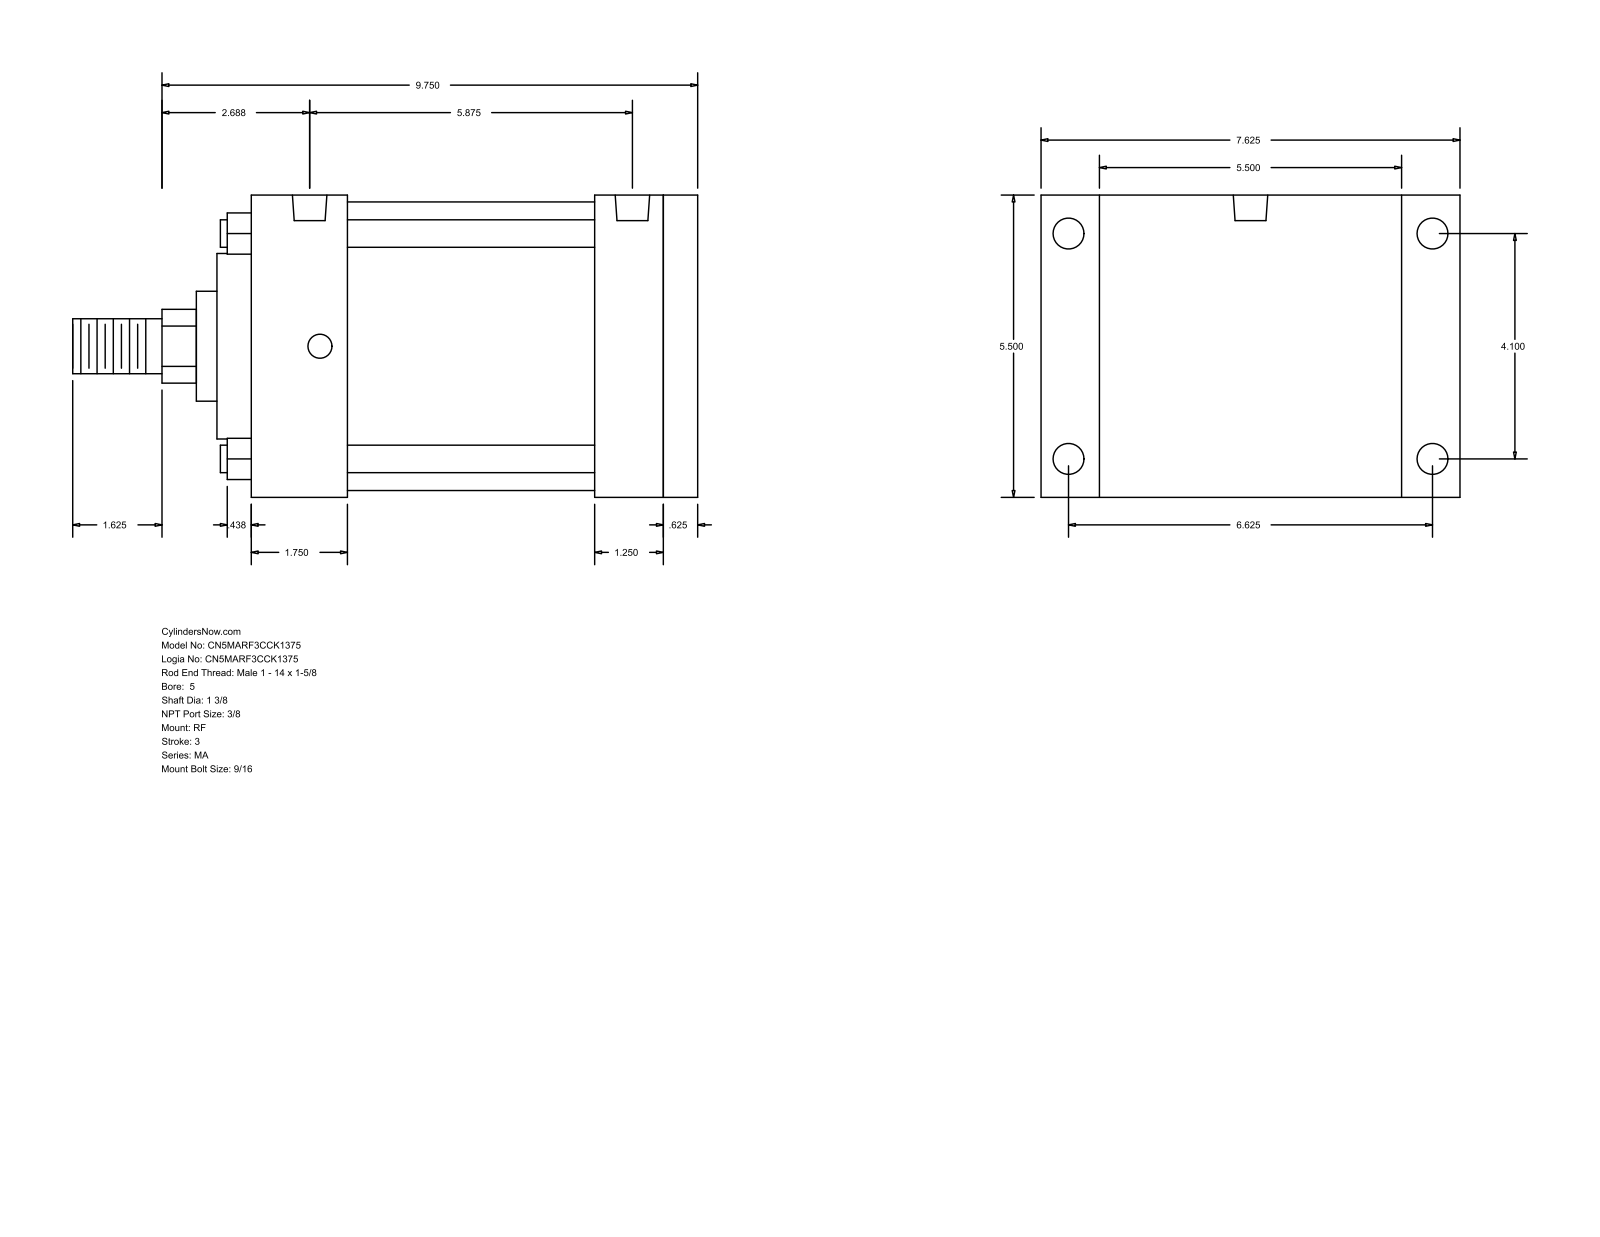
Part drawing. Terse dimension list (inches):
name: MA_RF__0500_1.375
written by: GSSL Pune (CONFIG_CONTROL_DESIGN)
unit: in
bodies: 0 solids, 94 faces (65 planar, 29 cylindrical, 0 other)
size: 11.375 × 7.625 × 5.5
holes: 4× ⌀0.437, 4× ⌀0.563, 2× ⌀0.627
bosses: 4× ⌀0.5, 1× ⌀5.25, 1× ⌀3.375, 1× ⌀2, 1× ⌀1.375, 1× ⌀1
rounds: 1× R0.672
face distances: 5.5, 8.125, 0.625, 7.5, 1.75, 5.75, 6.375, 6.25, 4.5, 1.25
hole spacings: 0.188, 4.1, 5.5, 5.687, 6.625, 7.791, 5.875
